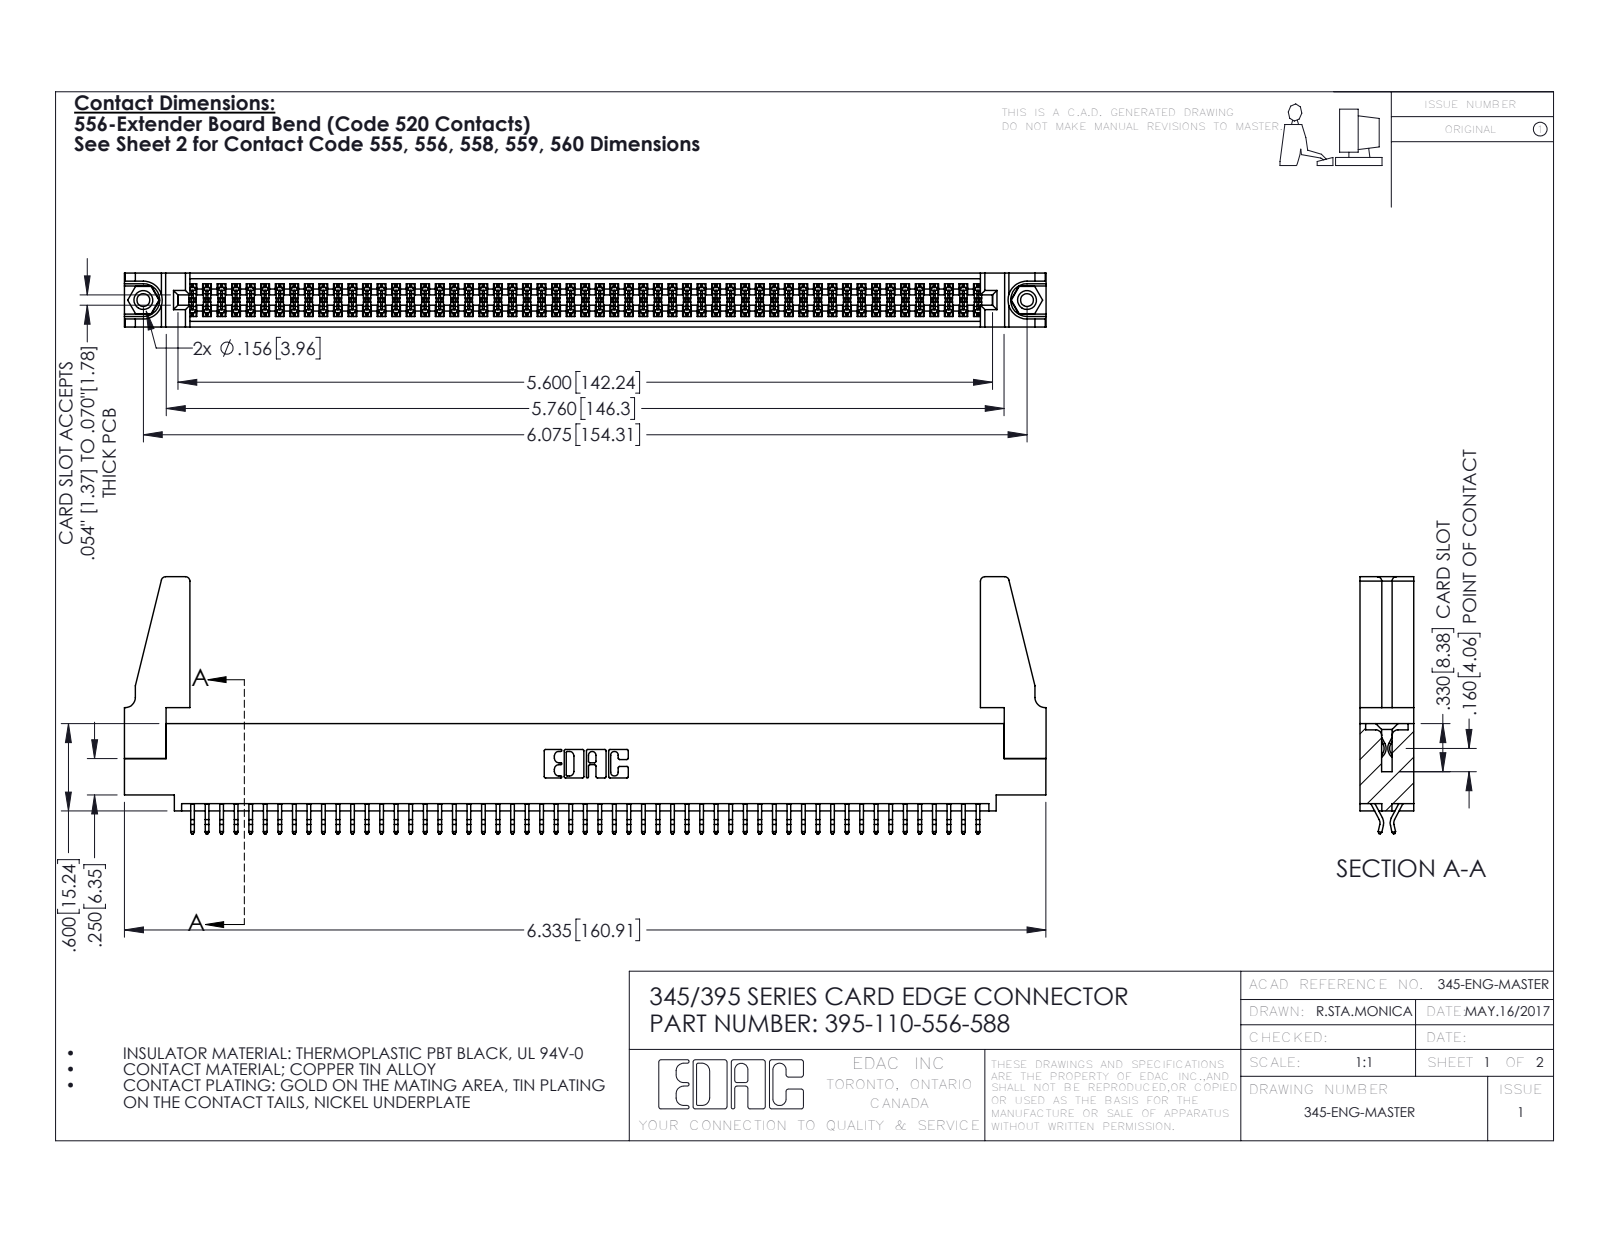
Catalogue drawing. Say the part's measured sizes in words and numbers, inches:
The part is named "345 Part_0.110 Offset - 0.156 Dia-TH; 345-250-001_345-250-001-102; 395-110-556-588; 345-220-078_345-220-088 (+1 more)". Its 3-D file was written by "SolidWorks 2016 (CONFIG_CONTROL_DESIGN)". It is 115 solids with 6414 faces: 4226 planar, 2172 cylindrical and 16 other. Overall it measures 6.336 by 1.767 by 0.37 inches. Its volume is 1.155 cubic inches and its surface area 41.14 square inches. Round holes: 2 of diameter 0.089, 2 of diameter 0.125, 2 of diameter 0.156, 1 of diameter 0.064. Round bosses or shafts: 2 of diameter 0.155. Partial cylindrical surfaces (rounded edges, fillets, slot ends): 165 of radius 0.006, 22 of radius 0.01, 8 of radius 0.03, 6 of radius 0.007, 6 of radius 0.031, 3 of radius 0.026, 2 of radius 0.01, 2 of radius 0.014. The main face-to-face distances are 0.072, 0.298, 0.37, 0.025, 0.2, 0.098, 0.272, 0.225, 0.175, 0.149. The hole center spacings are 0.27, 5.839, 6.075.
